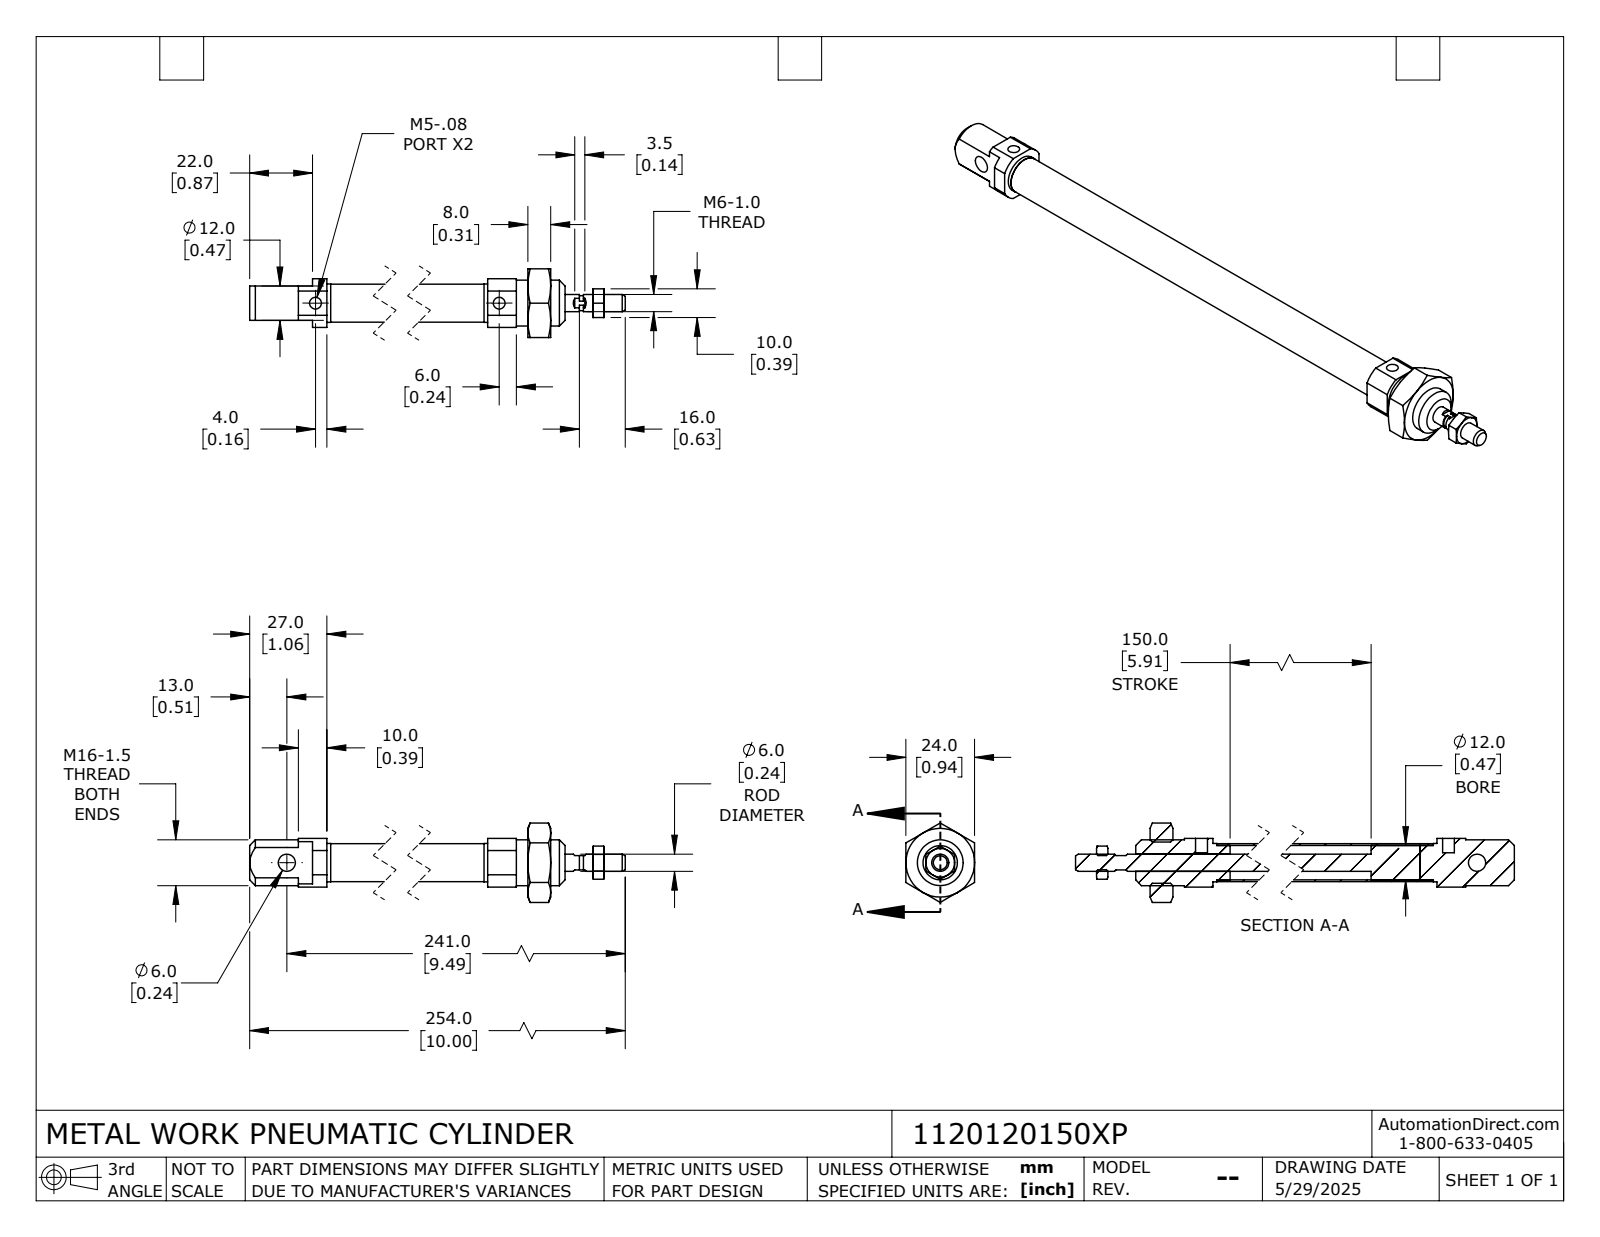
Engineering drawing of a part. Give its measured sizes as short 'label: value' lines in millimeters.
name: 1120120150XP; 1120120150XP_ROD; 1120120150XP_BODY
written by: SolidWorks 2024 (CONFIG_CONTROL_DESIGN)
unit: mm
bodies: 6 solids, 139 faces (56 planar, 45 cylindrical, 38 other)
size: 254 × 27.71 × 24
volume: 26 148 mm³; area: 25 797 mm²
holes: 2× ⌀4.13, 1× ⌀4.92, 1× ⌀6, 1× ⌀14.38
bosses: 1× ⌀16, 1× ⌀13.4, 1× ⌀13.27, 1× ⌀12, 1× ⌀6, 1× ⌀5.2
rounds: 1× R9.5
face distances: 17, 6, 24, 12, 206, 2.5, 14.5, 8, 3.5, 33
hole spacings: 187
